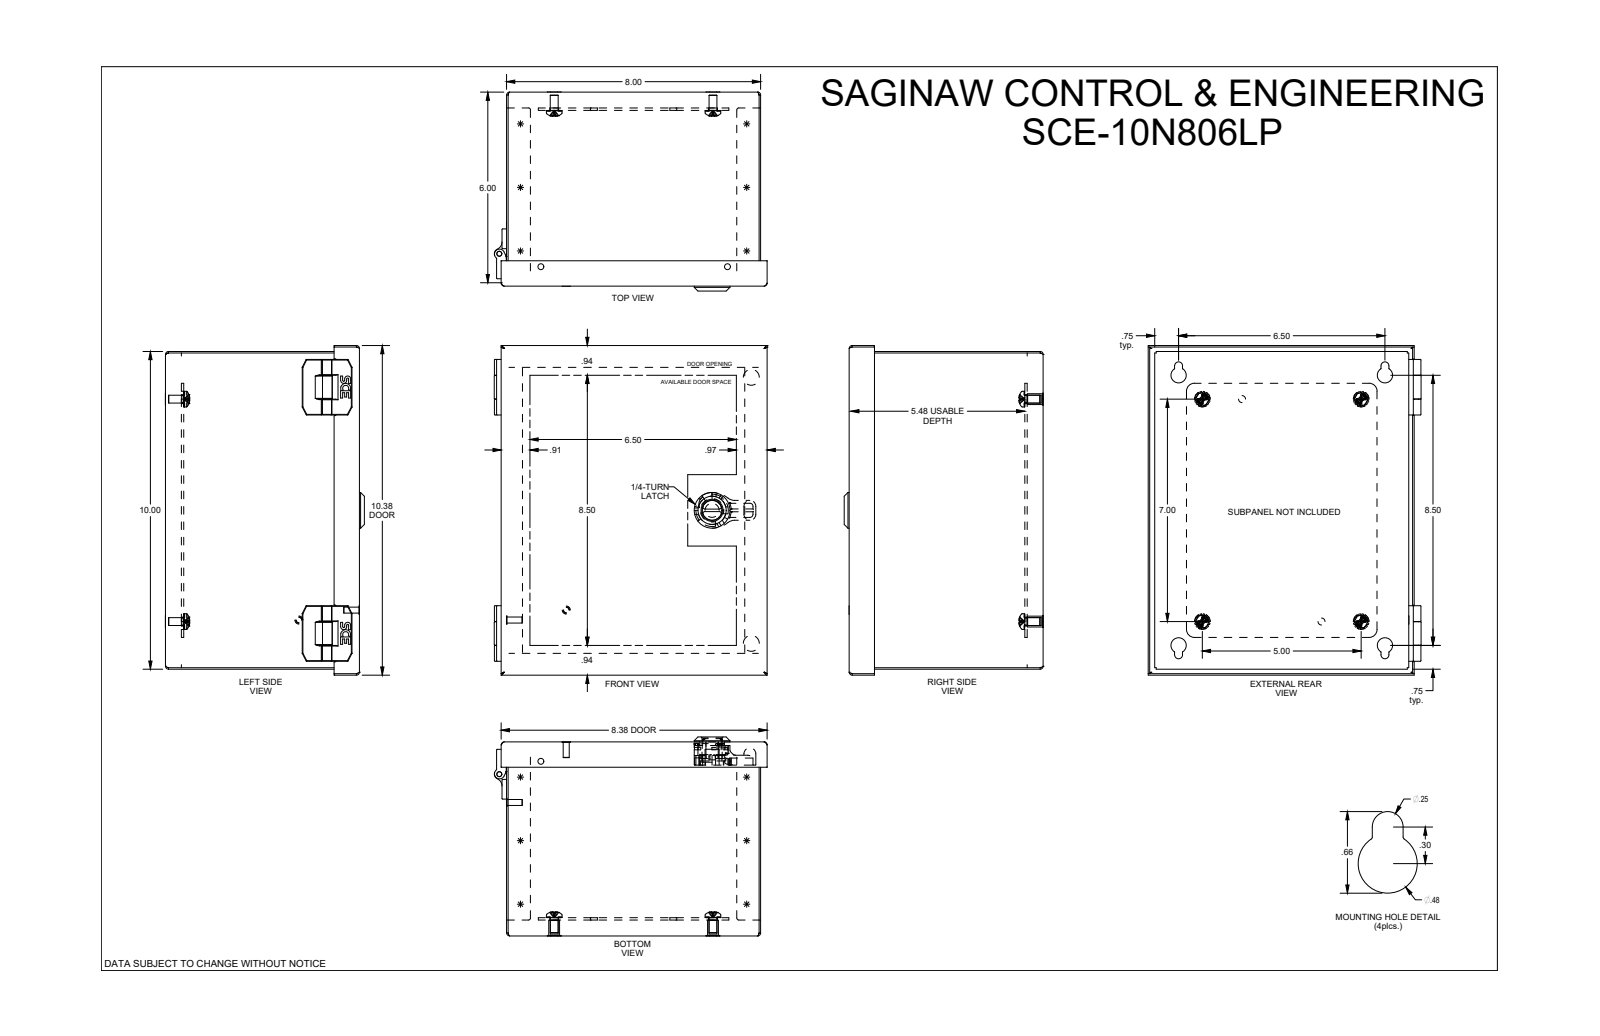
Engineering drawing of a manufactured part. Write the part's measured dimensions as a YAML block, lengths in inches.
part_name: "SCE-10N806LP"
step_written_by: "SolidWorks 2019 (AUTOMOTIVE_DESIGN)"
units: inches
bodies: {solids: 31, faces: 2413, planar: 710, cylindrical: 851, other: 852}
overall_size: [10.375, 8.593, 6.267]
volume: 30.73
surface_area: 986.4
round_holes:
  - {diameter: 0.17, count: 4}
  - {diameter: 0.25, count: 4}
  - {diameter: 0.281, count: 4}
  - {diameter: 0.329, count: 4}
  - {diameter: 0.343, count: 4}
  - {diameter: 0.48, count: 4}
  - {diameter: 0.193, count: 3}
  - {diameter: 0.218, count: 2}
  - {diameter: 0.158, count: 1}
  - {diameter: 0.187, count: 1}
  - {diameter: 0.44, count: 1}
  - {diameter: 0.635, count: 1}
round_bosses_or_shafts:
  - {diameter: 0.492, count: 4}
  - {diameter: 0.479, count: 4}
  - {diameter: 0.341, count: 4}
  - {diameter: 0.248, count: 4}
  - {diameter: 0.237, count: 4}
  - {diameter: 0.16, count: 4}
  - {diameter: 0.5, count: 2}
  - {diameter: 0.323, count: 2}
partial_cylinders:
  - {radius: 0.01, count: 253}
  - {radius: 0.106, count: 132}
  - {radius: 0.02, count: 95}
  - {radius: 0.005, count: 76}
  - {radius: 0.06, count: 25}
  - {radius: 0.015, count: 24}
  - {radius: 0.025, count: 24}
  - {radius: 0.055, count: 6}
face_to_face_distances: [0.06, 6.047, 7.94, 9.94, 5.987, 6.107, 8, 7.88, 0.5, 0.44]
hole_center_spacings: [1.061, 5.799, 7.75, 7.786, 9.65, 7.75, 7.826, 0.555]
